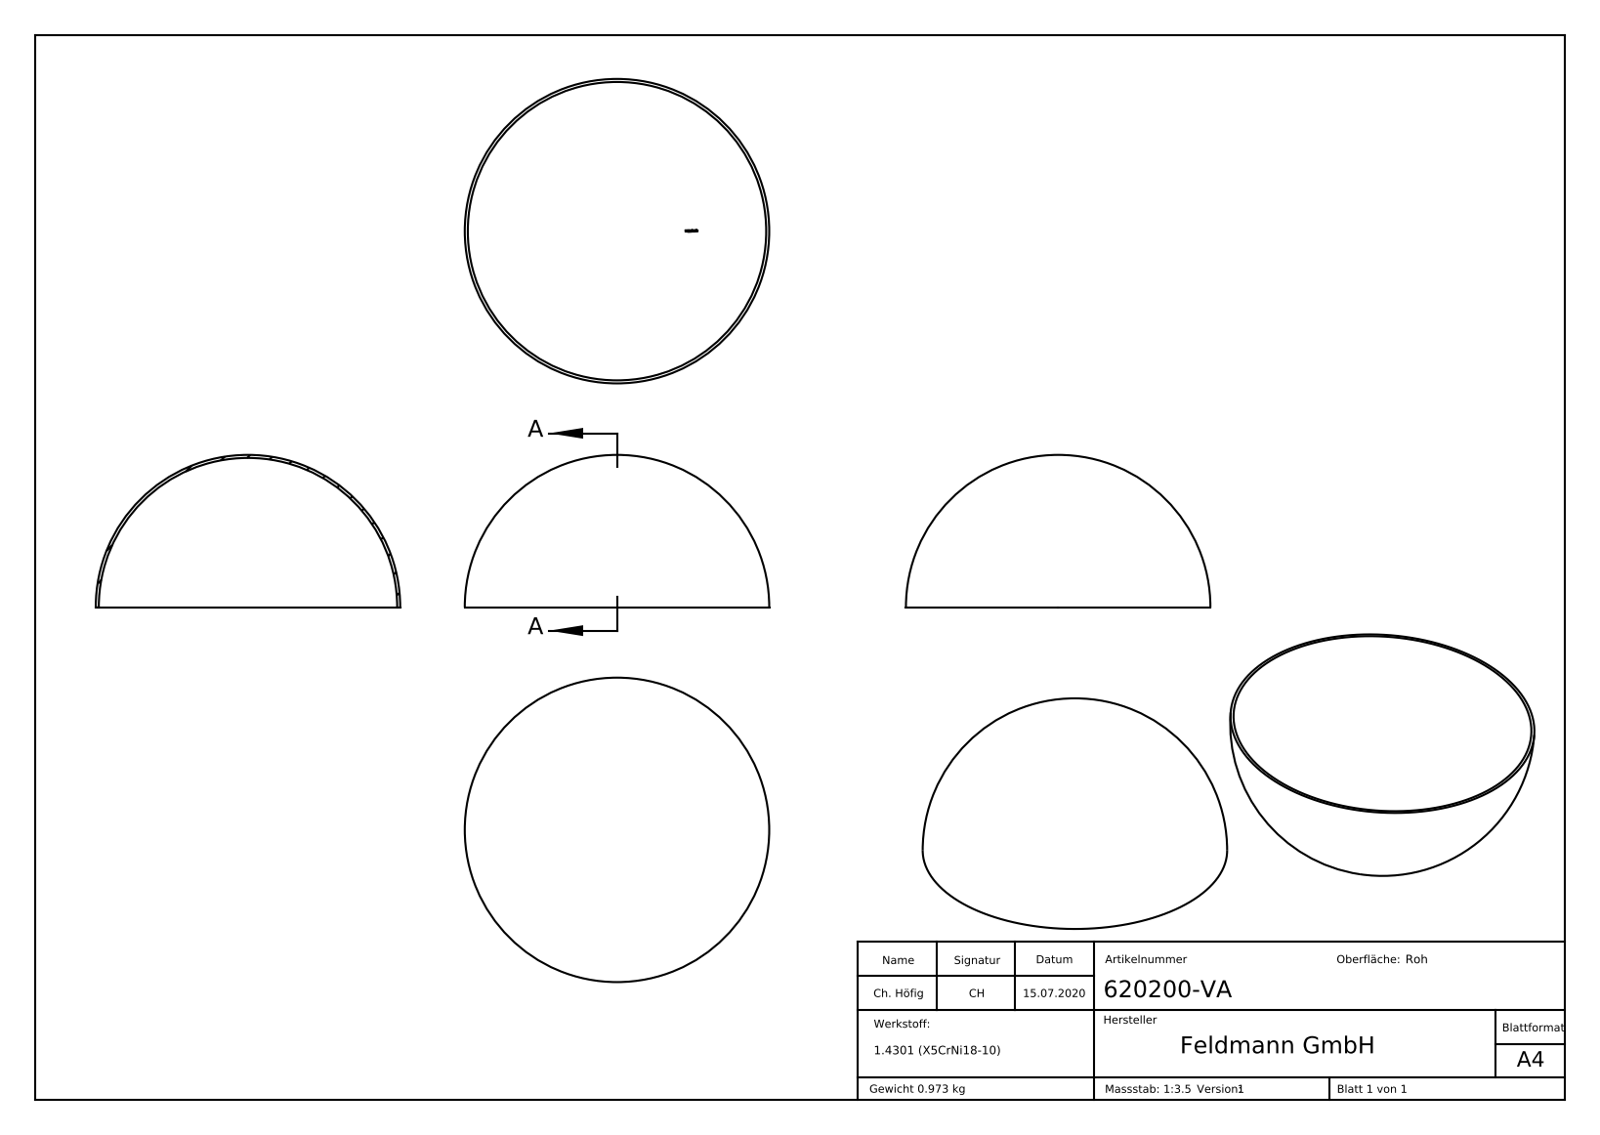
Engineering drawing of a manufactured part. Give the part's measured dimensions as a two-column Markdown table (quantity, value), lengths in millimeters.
| quantity | value |
| --- | --- |
| part name | 620200-VA |
| STEP written by | SolidWorks 2018 (CONFIG_CONTROL_DESIGN) |
| units | millimeters |
| bodies | 1 solid, 215 faces (92 planar, 0 cylindrical, 123 other) |
| overall size | 200 × 200 × 100 |
| volume | 123 167 mm³ |
| surface area | 124 424 mm² |
| main face-to-face distances | 0.45, 0.55, 0.5, 0.61, 1.19, 0.53, 0.81, 1.31, 0.85, 0.31 |
